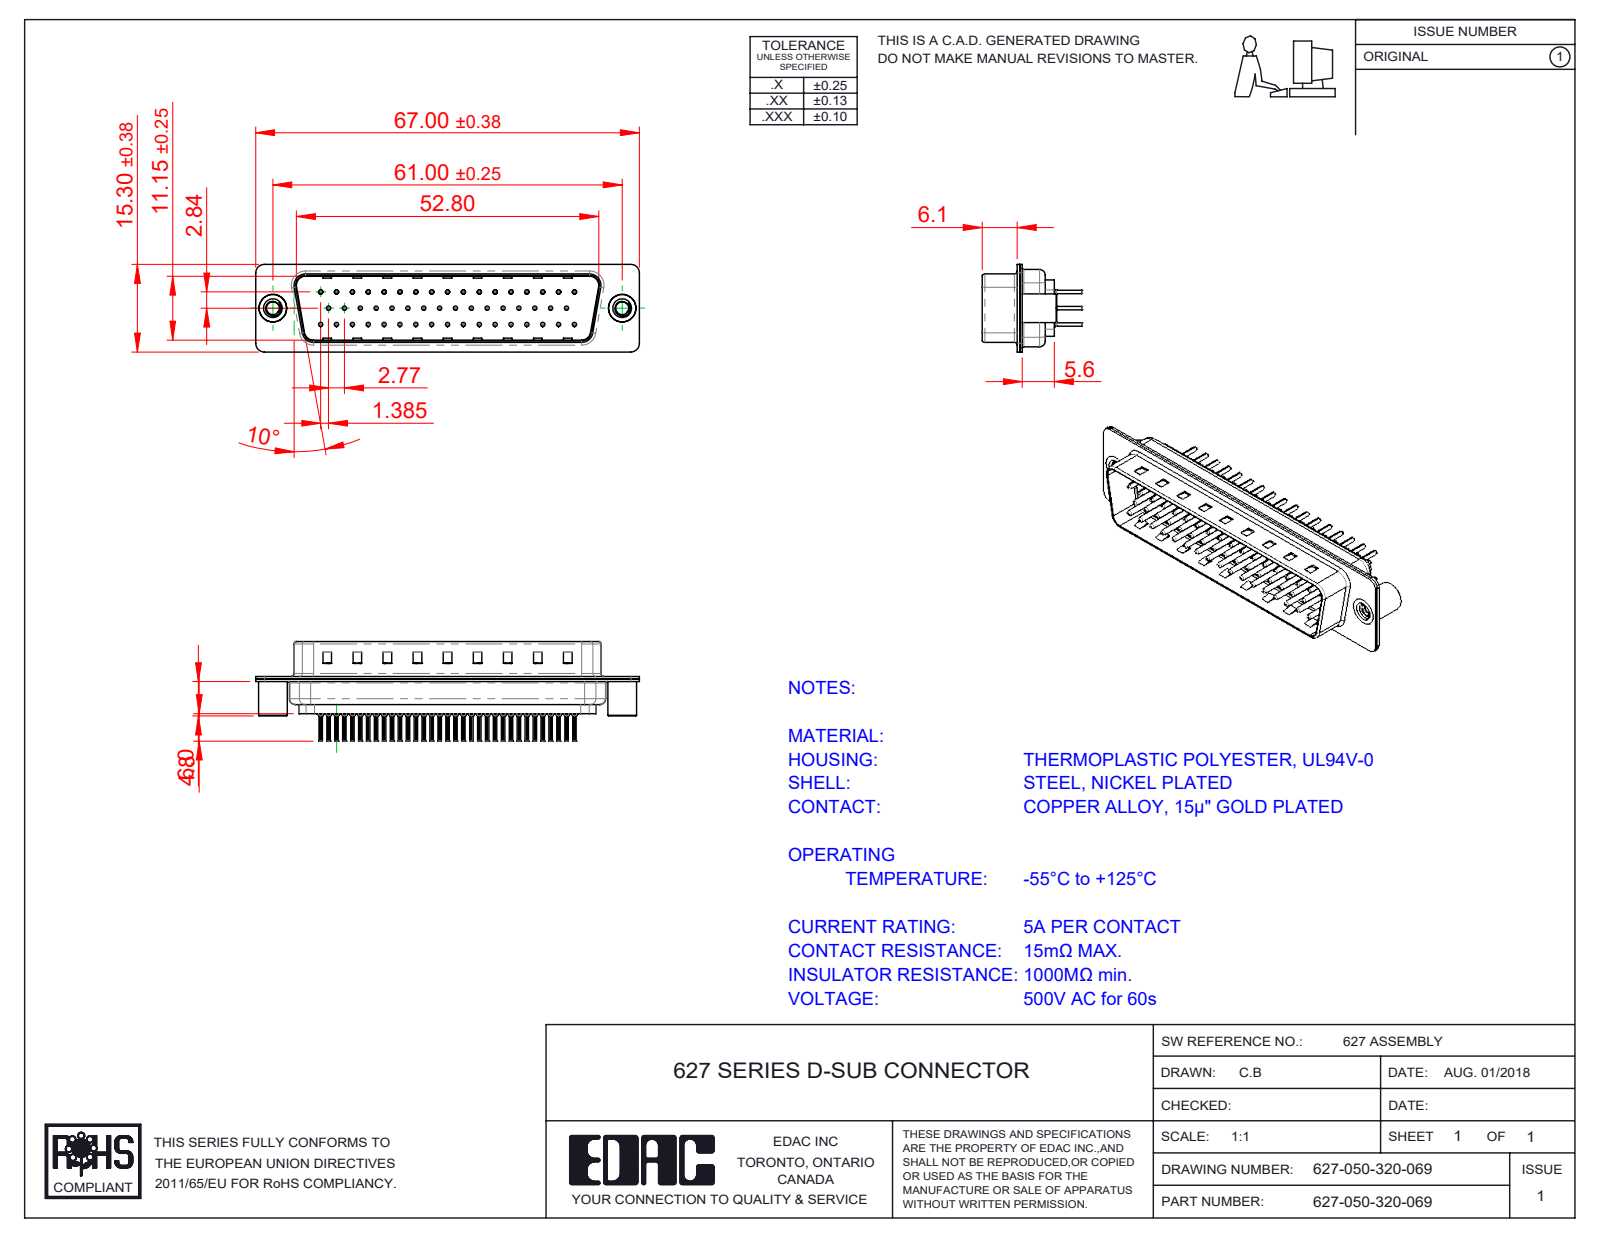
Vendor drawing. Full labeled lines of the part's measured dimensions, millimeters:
Part name (STEP PRODUCT): 627 Contact Row 2_20L; 627 Shell Front_50 Contacts; 627 4-40 Threaded Standoff BS; 627 Contact Row 1_20L (+4 more)
STEP written by: SolidWorks 2020 (CONFIG_CONTROL_DESIGN)
Units: millimetres
Bodies: 55 solids, 5334 faces (1403 planar, 2011 cylindrical, 1920 other)
Overall size (bounding box): 67 × 17.3 × 15.3
Volume: 4 520 mm³ · Surface area: 12 775 mm²
Round holes (diameter × count): ⌀0.2 ×50, ⌀0.35 ×50, ⌀1.1 ×50, ⌀1.6 ×50, ⌀2.26 ×2, ⌀4 ×2, ⌀4.8 ×2
Round bosses / shafts (diameter × count): ⌀2 ×50, ⌀1.5 ×50, ⌀0.75 ×50, ⌀0.6 ×50, ⌀5 ×2, ⌀4.9 ×2
Partial cylindrical surfaces — rounded edges, fillets, slot ends (radius × count): R0.1 ×100, R1.5 ×16, R2 ×12, R0.5 ×8, R1.6 ×8, R0.25 ×4, R0.6 ×4, R0.65 ×4
Main face-to-face distances: 0.4, 0.45, 11.55, 0.9, 6.05, 6.5, 0.78, 12.33, 1.95, 0.77
Hole centre spacings: 3.16, 2.77, 5.54, 8.31, 11.08, 13.85, 16.62, 5.03
